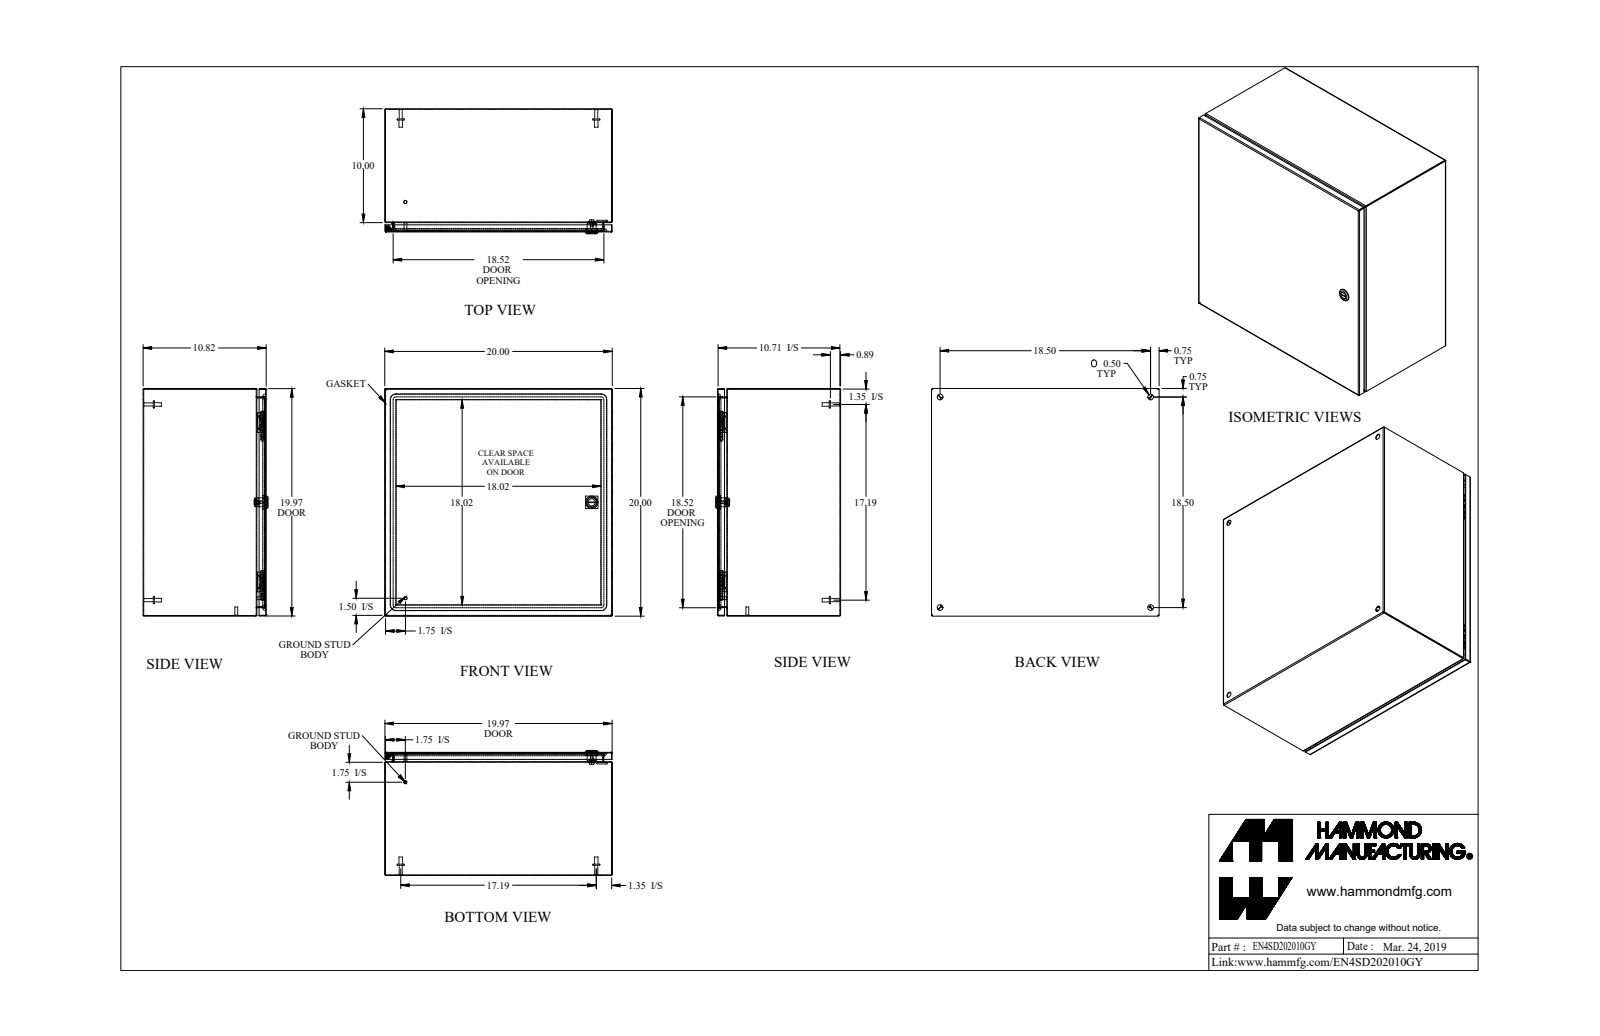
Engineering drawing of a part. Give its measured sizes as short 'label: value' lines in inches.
name: EN4SD202010GY_Default
written by: SolidWorks 2019 (CONFIG_CONTROL_DESIGN)
unit: in
bodies: 21 solids, 634 faces (285 planar, 213 cylindrical, 136 other)
size: 20 × 20 × 10.982
volume: 107.9 in³; area: 3 687 in²
holes: 4× ⌀0.5, 1× ⌀0.172, 1× ⌀0.232, 1× ⌀0.24, 1× ⌀0.242, 1× ⌀0.625, 1× ⌀0.785
bosses: 4× ⌀0.625, 4× ⌀0.313, 4× ⌀0.27, 2× ⌀0.281, 2× ⌀0.25, 1× ⌀1.1, 1× ⌀0.525, 1× ⌀0.455
rounds: 21× R0.029, 21× R0.086, 16× R0.25, 8× R19, 4× R0.006, 4× R0.062, 4× R0.499, 2× R0.125
face distances: 0.057, 10.765, 19.943, 19.886, 10.708, 10.822, 20, 0.822, 9.943, 0.749
hole spacings: 18.5, 26.163, 9.31, 9.311, 19.742, 19.742
